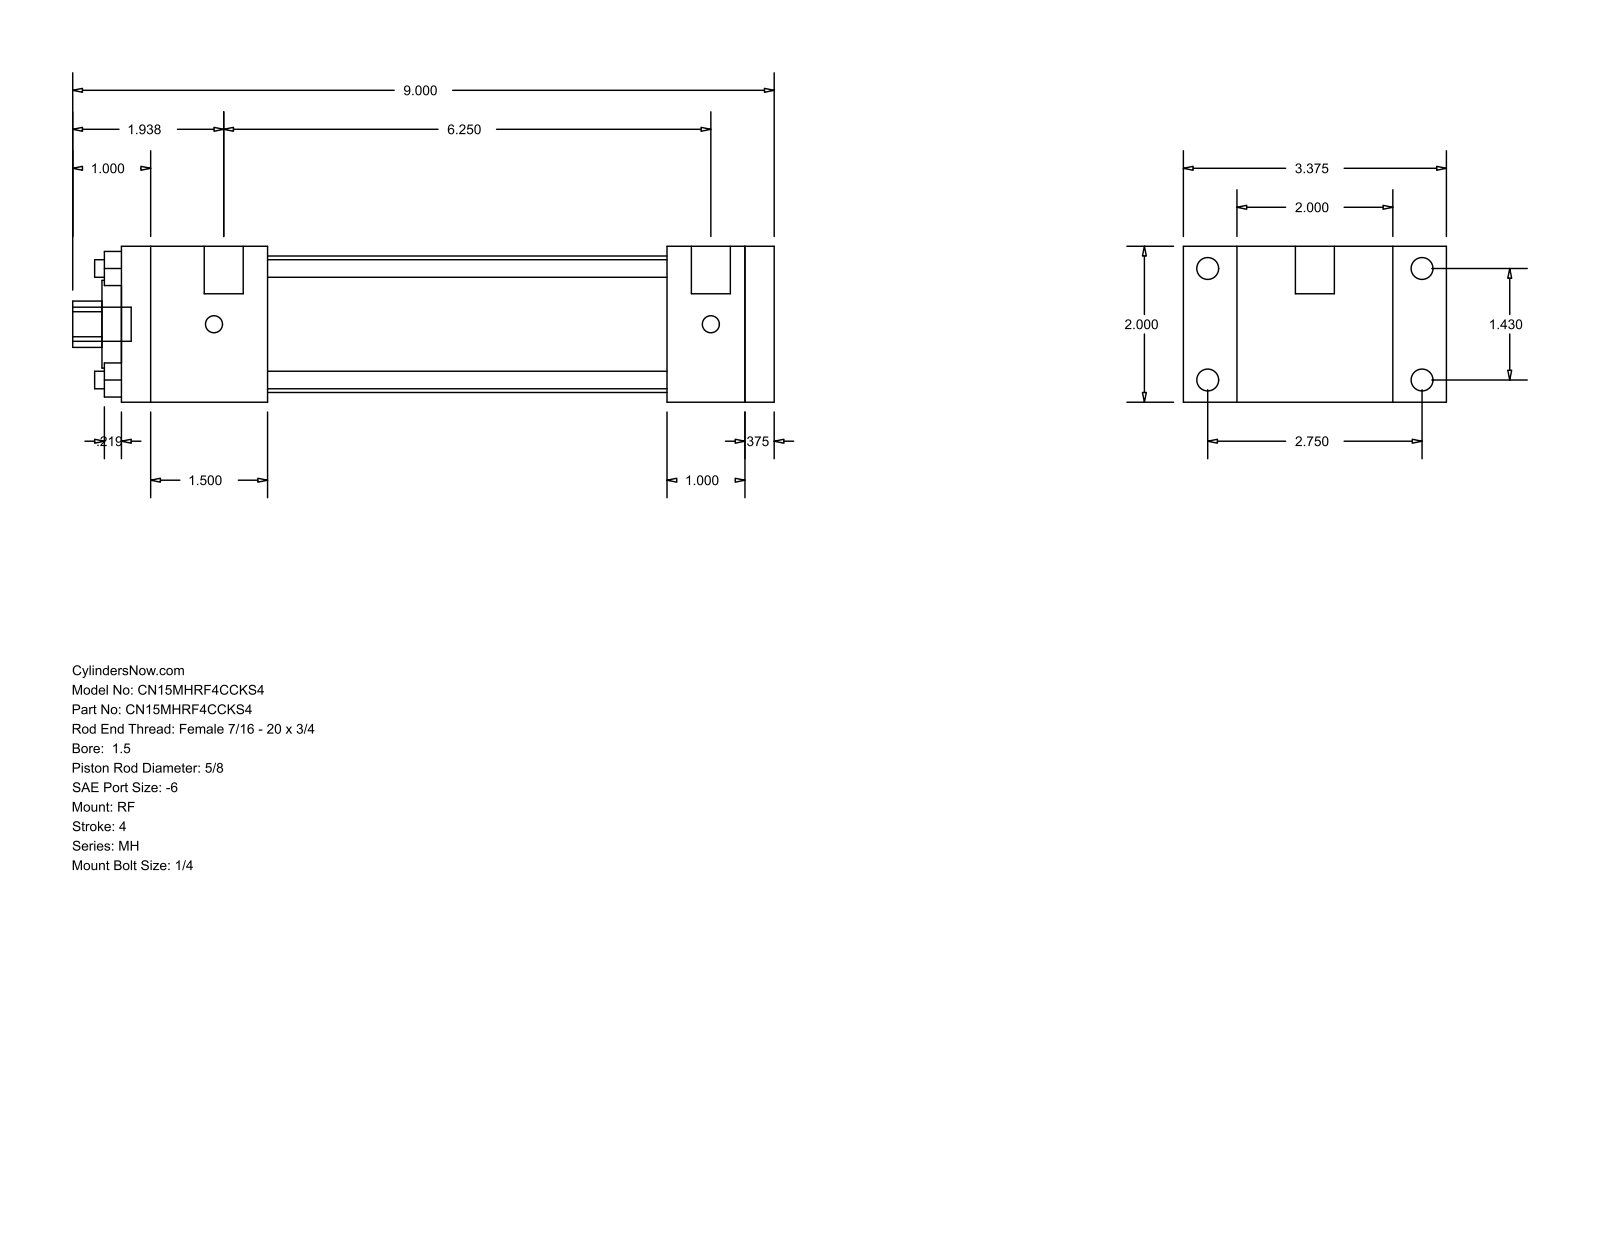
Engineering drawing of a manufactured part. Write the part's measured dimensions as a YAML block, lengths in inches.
part_name: "MH_RF__0150_0.625"
step_written_by: "GSSL Pune (CONFIG_CONTROL_DESIGN)"
units: inches
bodies: {solids: 0, faces: 92, planar: 64, cylindrical: 28, other: 0}
overall_size: [9, 3.375, 2]
round_holes:
  - {diameter: 0.225, count: 4}
  - {diameter: 0.625, count: 1}
  - {diameter: 1.125, count: 1}
  - {diameter: 1.75, count: 1}
round_bosses_or_shafts:
  - {diameter: 0.281, count: 4}
  - {diameter: 0.219, count: 4}
  - {diameter: 0.5, count: 2}
  - {diameter: 0.437, count: 1}
partial_cylinders:
  - {radius: 0.297, count: 1}
face_to_face_distances: [2, 0.375, 8.375, 8, 0.687, 2.687, 7, 1, 1.375, 1.875]
hole_center_spacings: [1.011, 1.43, 2.022]
